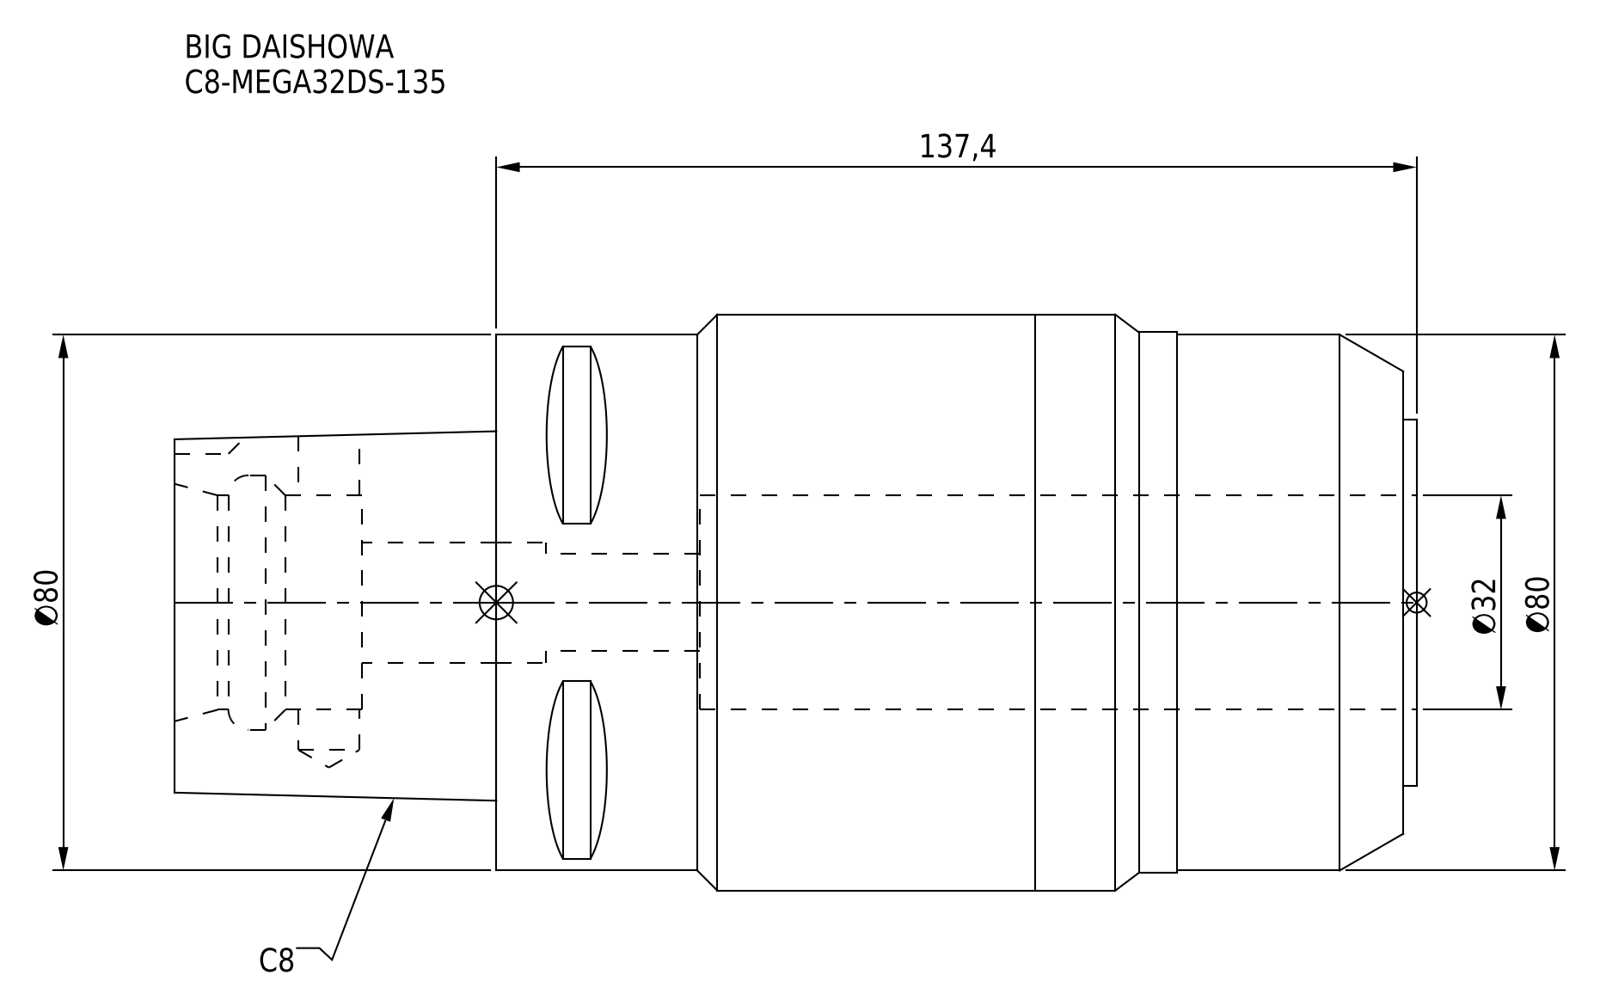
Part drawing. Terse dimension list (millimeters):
name: C8-MEGA32DS-135
written by: CREO PARAMETRIC BY PTC INC, 2016380 (AUTOMOTIVE_DESIGN)
unit: mm
bodies: 1 solid, 73 faces (30 planar, 27 cylindrical, 16 other)
size: 185.4 × 86 × 86
volume: 711 123 mm³; area: 70 110 mm²
holes: 1× ⌀9.1, 1× ⌀14.5, 1× ⌀18, 1× ⌀32, 1× ⌀38
bosses: 1× ⌀86, 1× ⌀80.7, 1× ⌀80, 1× ⌀54.7
rounds: 1× R6
face distances: 137.4, 2, 135.4, 185.4, 183.4, 48, 107, 105, 30.4, 78.4
